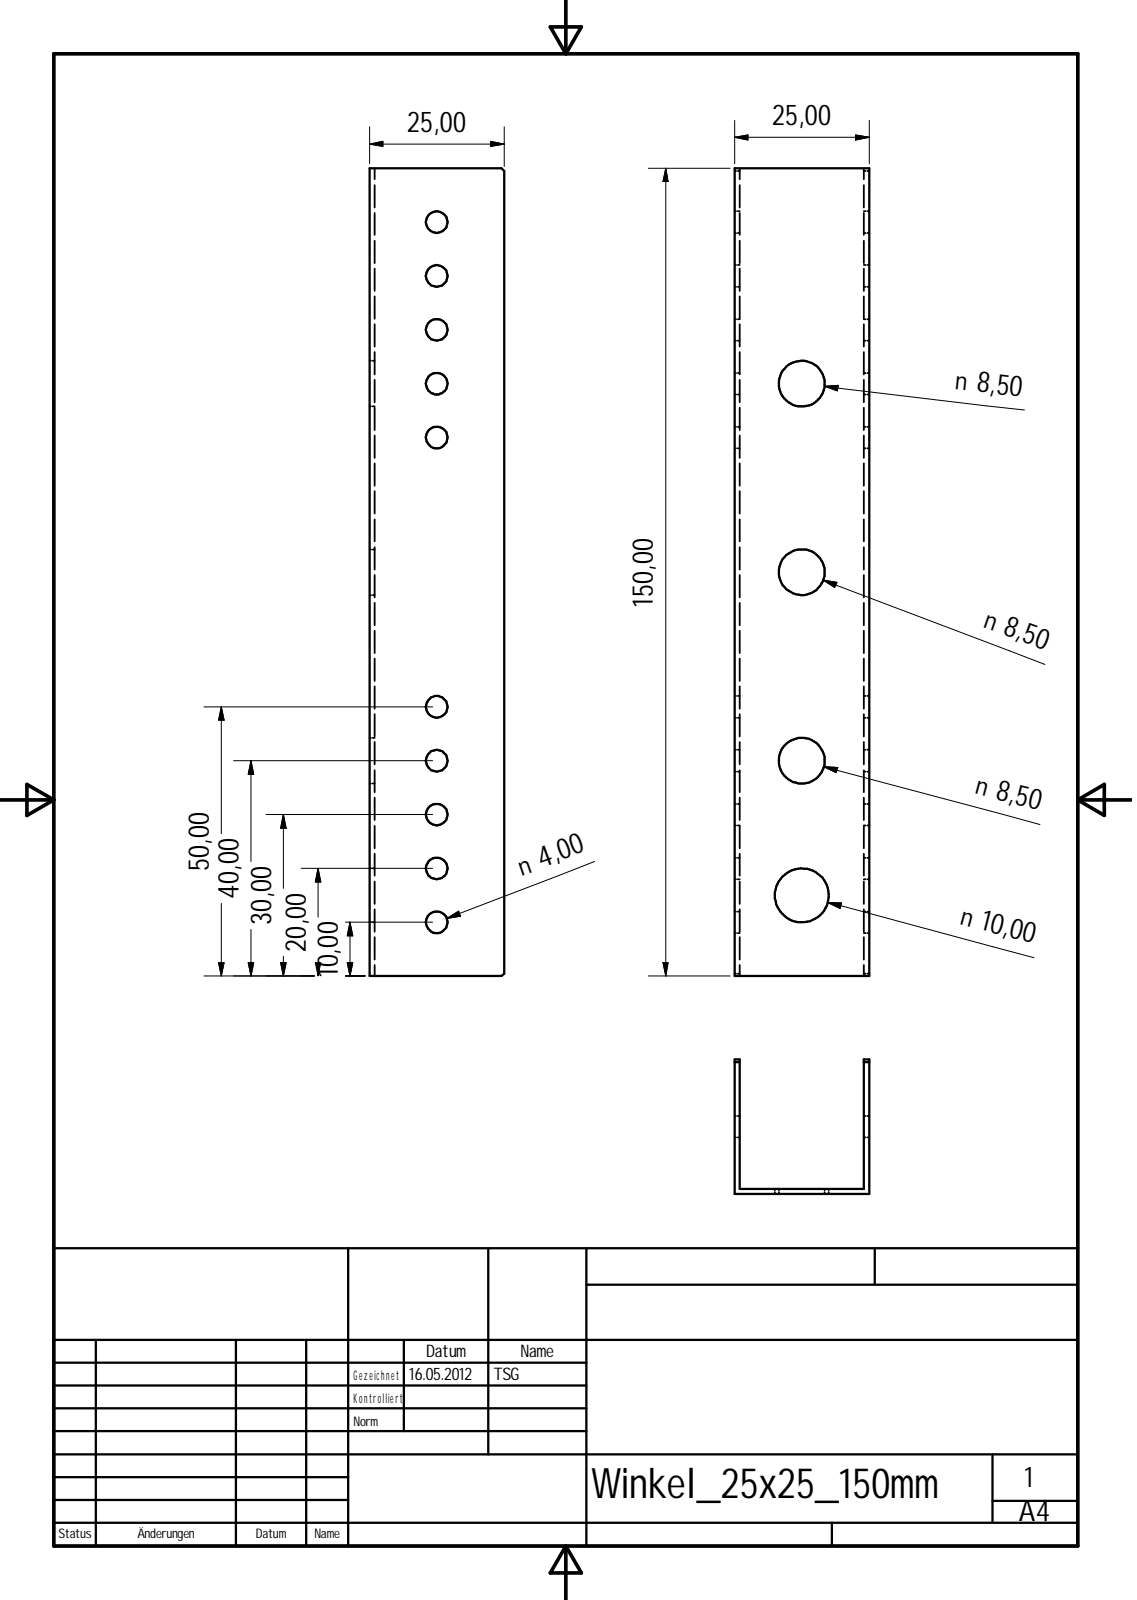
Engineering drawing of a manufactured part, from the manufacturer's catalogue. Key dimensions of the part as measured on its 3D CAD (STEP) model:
Part name (STEP PRODUCT): Startrampe_Grundk\S\vrper.iam (Detailgenauigkeit1); Deckplatte; Gewindestange_M8_100mm; Grundplatte (+7 more)
STEP written by: unknown (AUTOMOTIVE_DESIGN)
Units: millimetres
Bodies: 159 solids, 1733 faces (1004 planar, 94 cylindrical, 635 other)
Overall size (bounding box): 341.59 × 295.82 × 217
Volume: 1 684 000 mm³ · Surface area: 495 827 mm²
Round holes (diameter × count): ⌀8.4 ×9, ⌀13 ×1, ⌀15 ×1, ⌀50 ×1
Round bosses / shafts (diameter × count): ⌀24 ×9, ⌀16 ×9, ⌀8 ×9
Main face-to-face distances: 19, 159, 1, 140, 5, 14, 178, 21, 20, 18
Hole centre spacings: 35, 230.16, 169.78, 202.24, 70, 80, 115, 138.56
